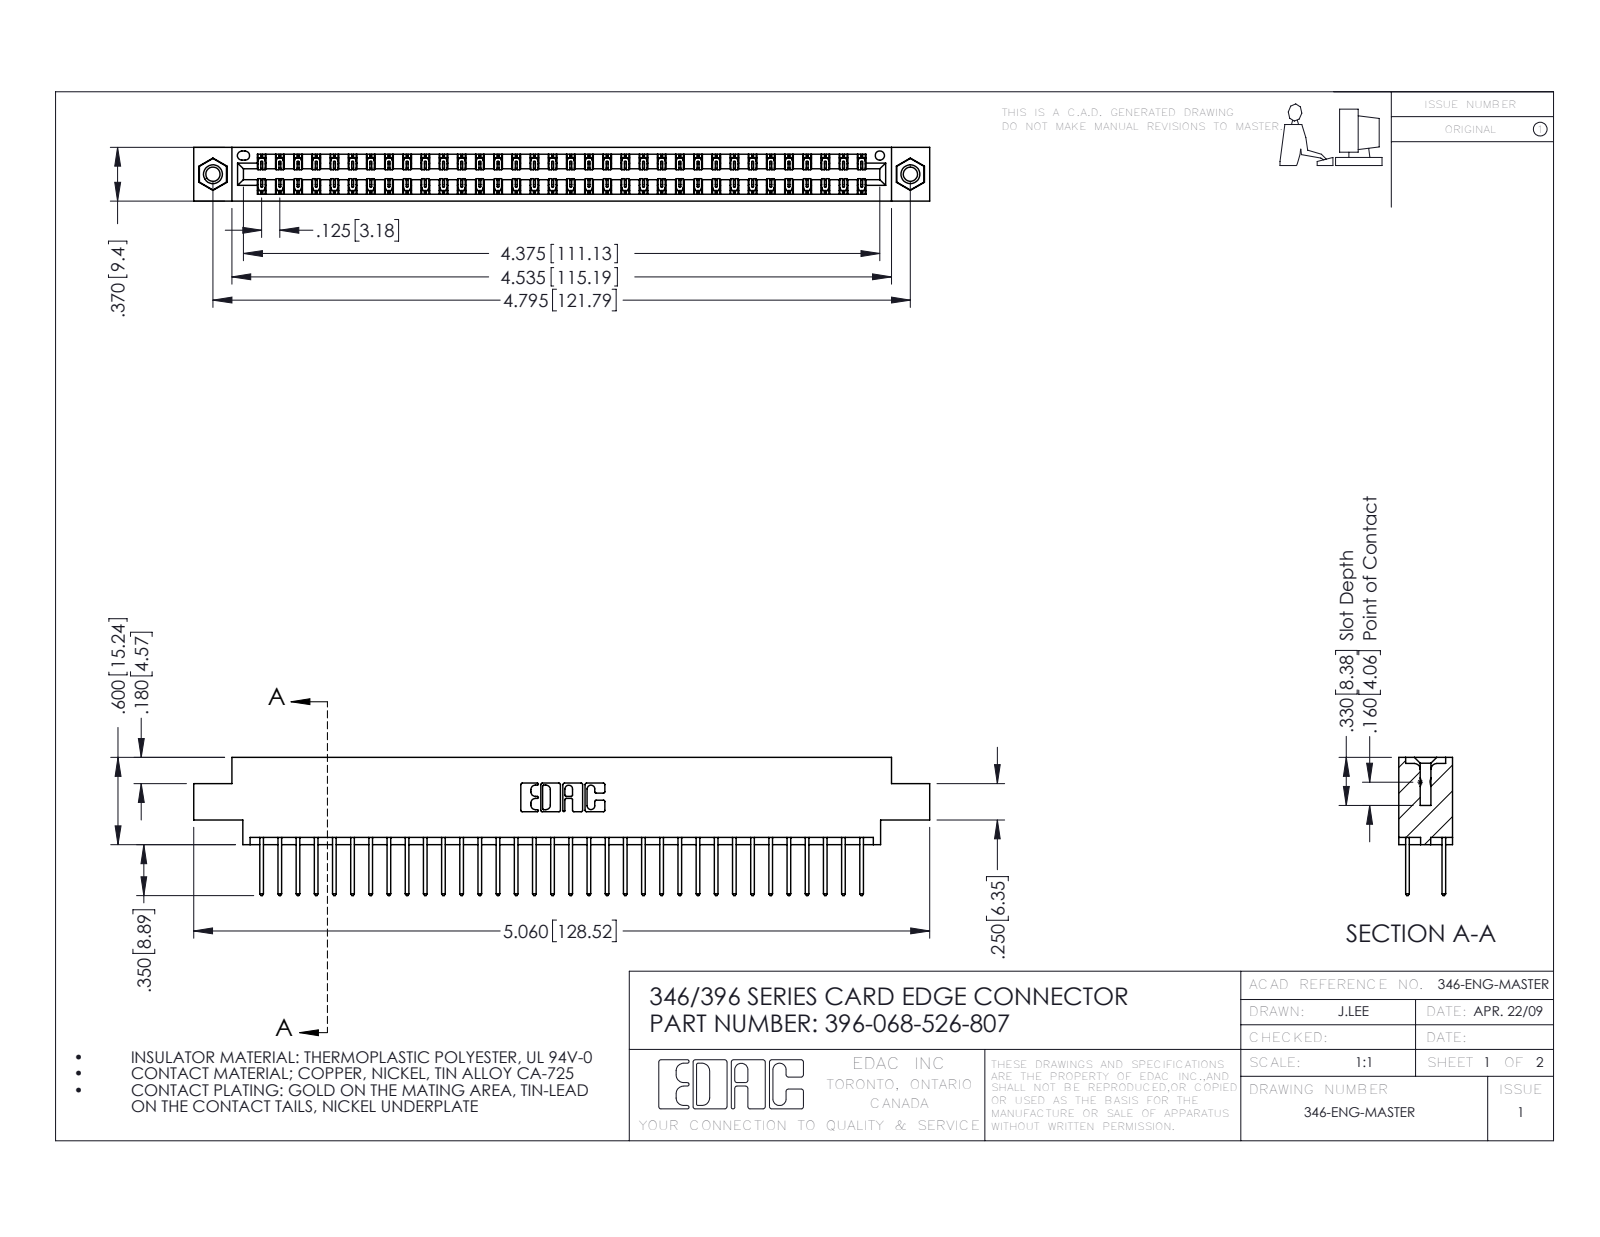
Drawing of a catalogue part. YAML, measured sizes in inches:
part_name: "396-068-526-807; 345-292-001_345-293-126; 345-250-001_345-250-005-103; 346 Part_0.170 Offset - 0.156 Dia-TI"
step_written_by: "SolidWorks 2016 (CONFIG_CONTROL_DESIGN)"
units: inches
bodies: {solids: 71, faces: 3722, planar: 2492, cylindrical: 1214, other: 16}
overall_size: [5.06, 0.95, 0.37]
volume: 0.758
surface_area: 27.36
round_holes:
  - {diameter: 0.098, count: 2}
  - {diameter: 0.125, count: 2}
  - {diameter: 0.156, count: 2}
  - {diameter: 0.064, count: 1}
round_bosses_or_shafts:
  - {diameter: 0.155, count: 2}
partial_cylinders:
  - {radius: 0.006, count: 102}
  - {radius: 0.01, count: 68}
  - {radius: 0.01, count: 22}
  - {radius: 0.007, count: 6}
  - {radius: 0.031, count: 6}
  - {radius: 0.026, count: 3}
  - {radius: 0.014, count: 2}
  - {radius: 0.022, count: 2}
face_to_face_distances: [0.048, 0.322, 0.25, 0.37, 0.072, 0.298, 0.025, 0.275, 0.222, 0.148]
hole_center_spacings: [0.246, 4.587, 4.795]
